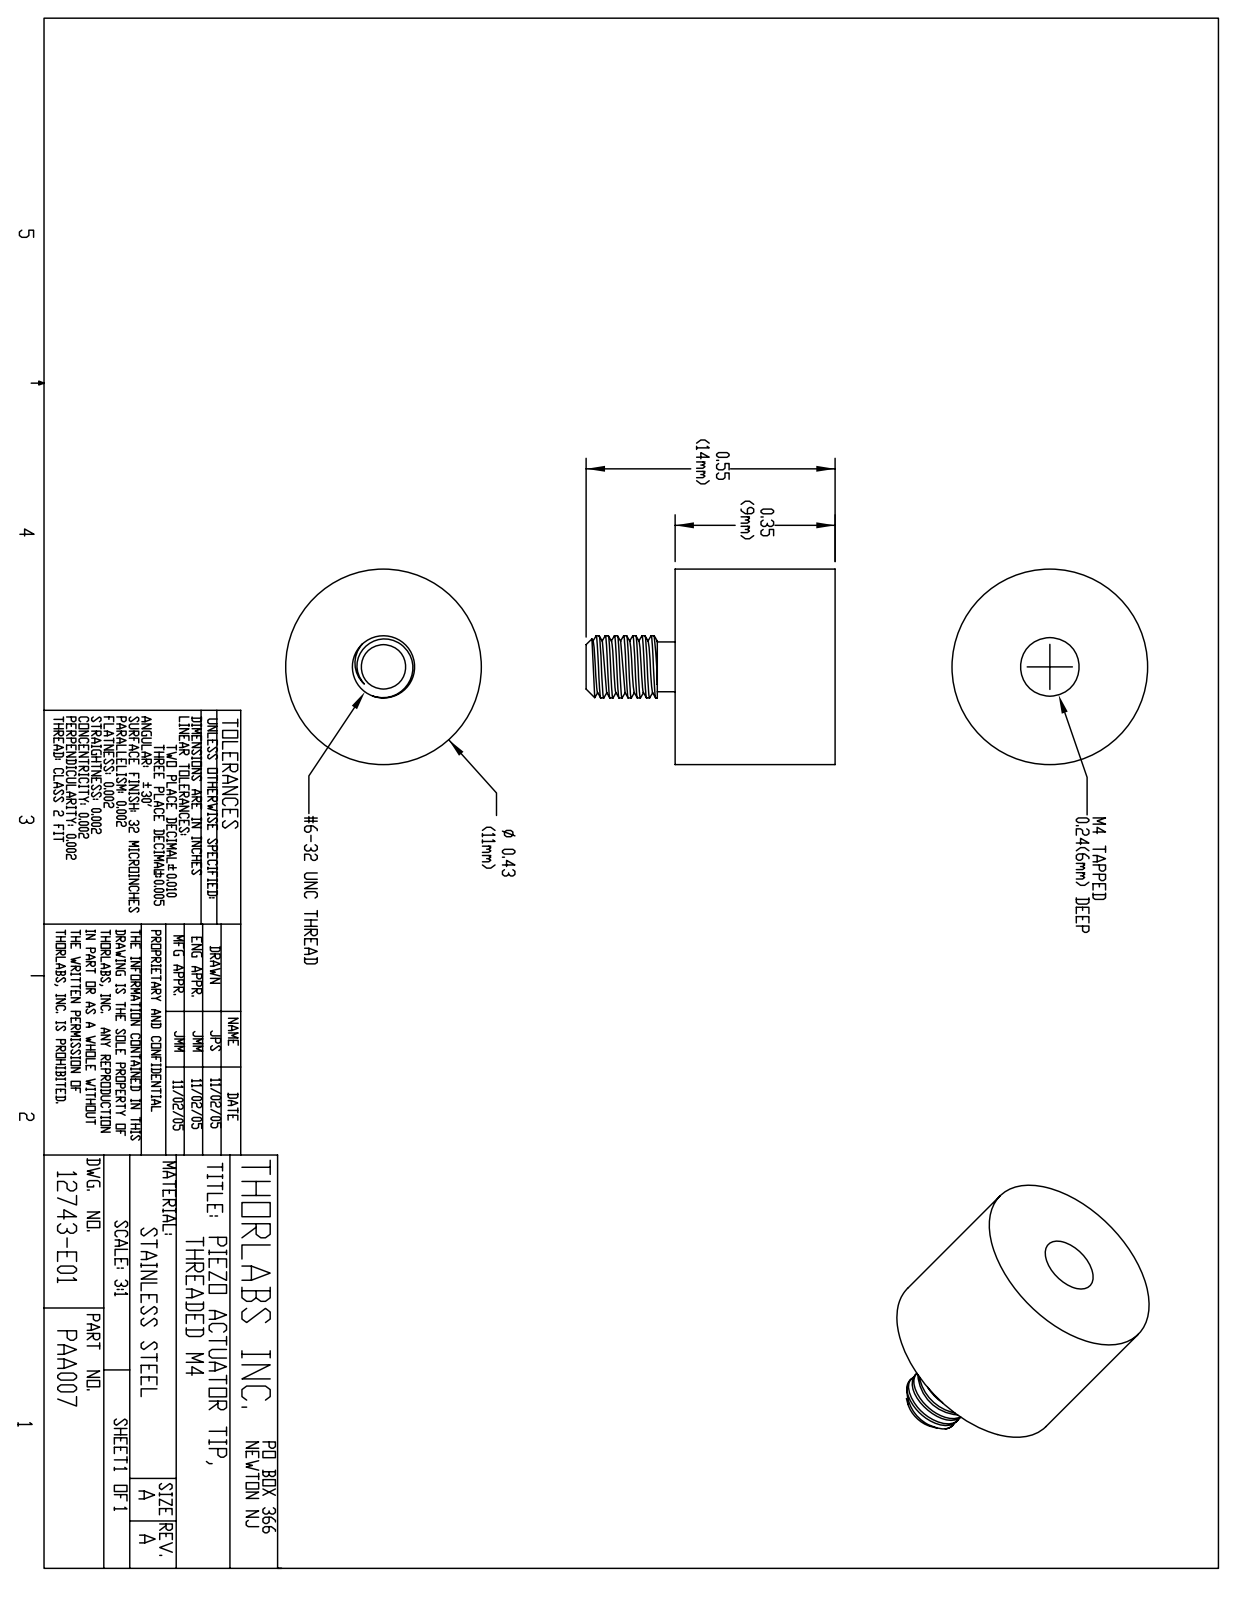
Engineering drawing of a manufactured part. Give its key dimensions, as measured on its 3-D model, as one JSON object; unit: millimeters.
{"part_name": "12743-E0W", "step_written_by": "SolidWorks 2007 (AUTOMOTIVE_DESIGN)", "units": "millimeters", "bodies": {"solids": 0, "faces": 28, "planar": 3, "cylindrical": 21, "other": 4}, "overall_size": [14, 11, 11], "round_holes": [[3.3, 1]], "round_bosses_or_shafts": [[11, 1], [3.5, 1], [2.8, 1]], "face_to_face_distances": [9, 14, 5]}
